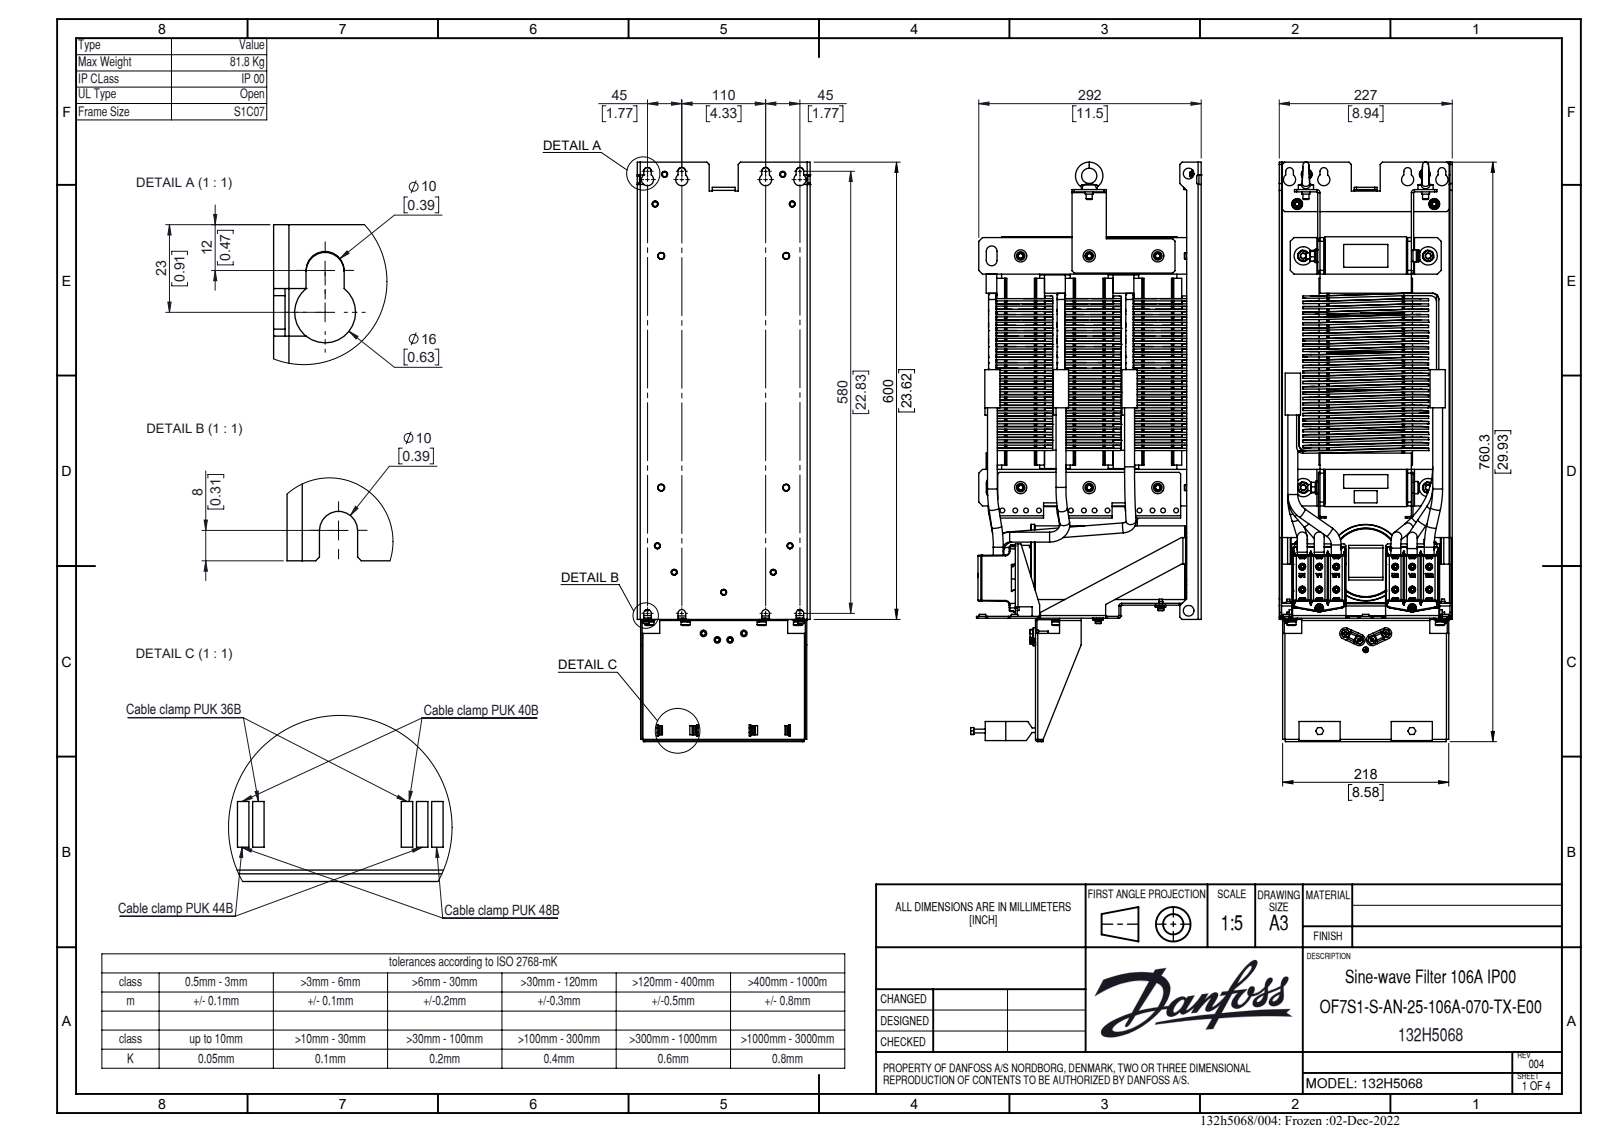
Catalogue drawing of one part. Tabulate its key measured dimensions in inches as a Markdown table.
| quantity | value |
| --- | --- |
| part name | 132H5068-V002-220222_OUT |
| STEP written by | CREO PARAMETRIC BY PTC INC, 2020342 (CONFIG_CONTROL_DESIGN) |
| units | inches |
| bodies | 6 solids, 2514 faces (1499 planar, 695 cylindrical, 320 other) |
| overall size | 29.933 × 11.909 × 8.937 |
| volume | 839.1 in³ |
| surface area | 2 327 in² |
| round holes (diameter × count) | 0.244 × 14, 0.316 × 12, 0.197 × 8, 0.165 × 6, 0.256 × 6, 0.276 × 5, 0.331 × 4, 0.624 × 3, 0.236 × 2, 0.268 × 2, 0.551 × 2, 0.281 × 1 |
| round bosses / shafts (diameter × count) | 0.315 × 28, 0.236 × 22, 0.276 × 6, 0.63 × 5, 0.945 × 4, 0.591 × 4, 0.583 × 4, 0.455 × 4 |
| partial cylindrical surfaces (radius × count) | 0.039 × 40, 0.118 × 26, 0.138 × 20, 0.217 × 12, 0.177 × 10, 0.197 × 8, 0.157 × 7, 0.315 × 6 |
| main face-to-face distances | 0.118, 0.079, 0.098, 0.059, 1.988, 6.457, 8.563, 1.929, 2.185, 7.847 |
| hole center spacings | 4.803, 0.878, 1.472, 3.543, 0.669, 1.181, 1.22, 4.946 |
